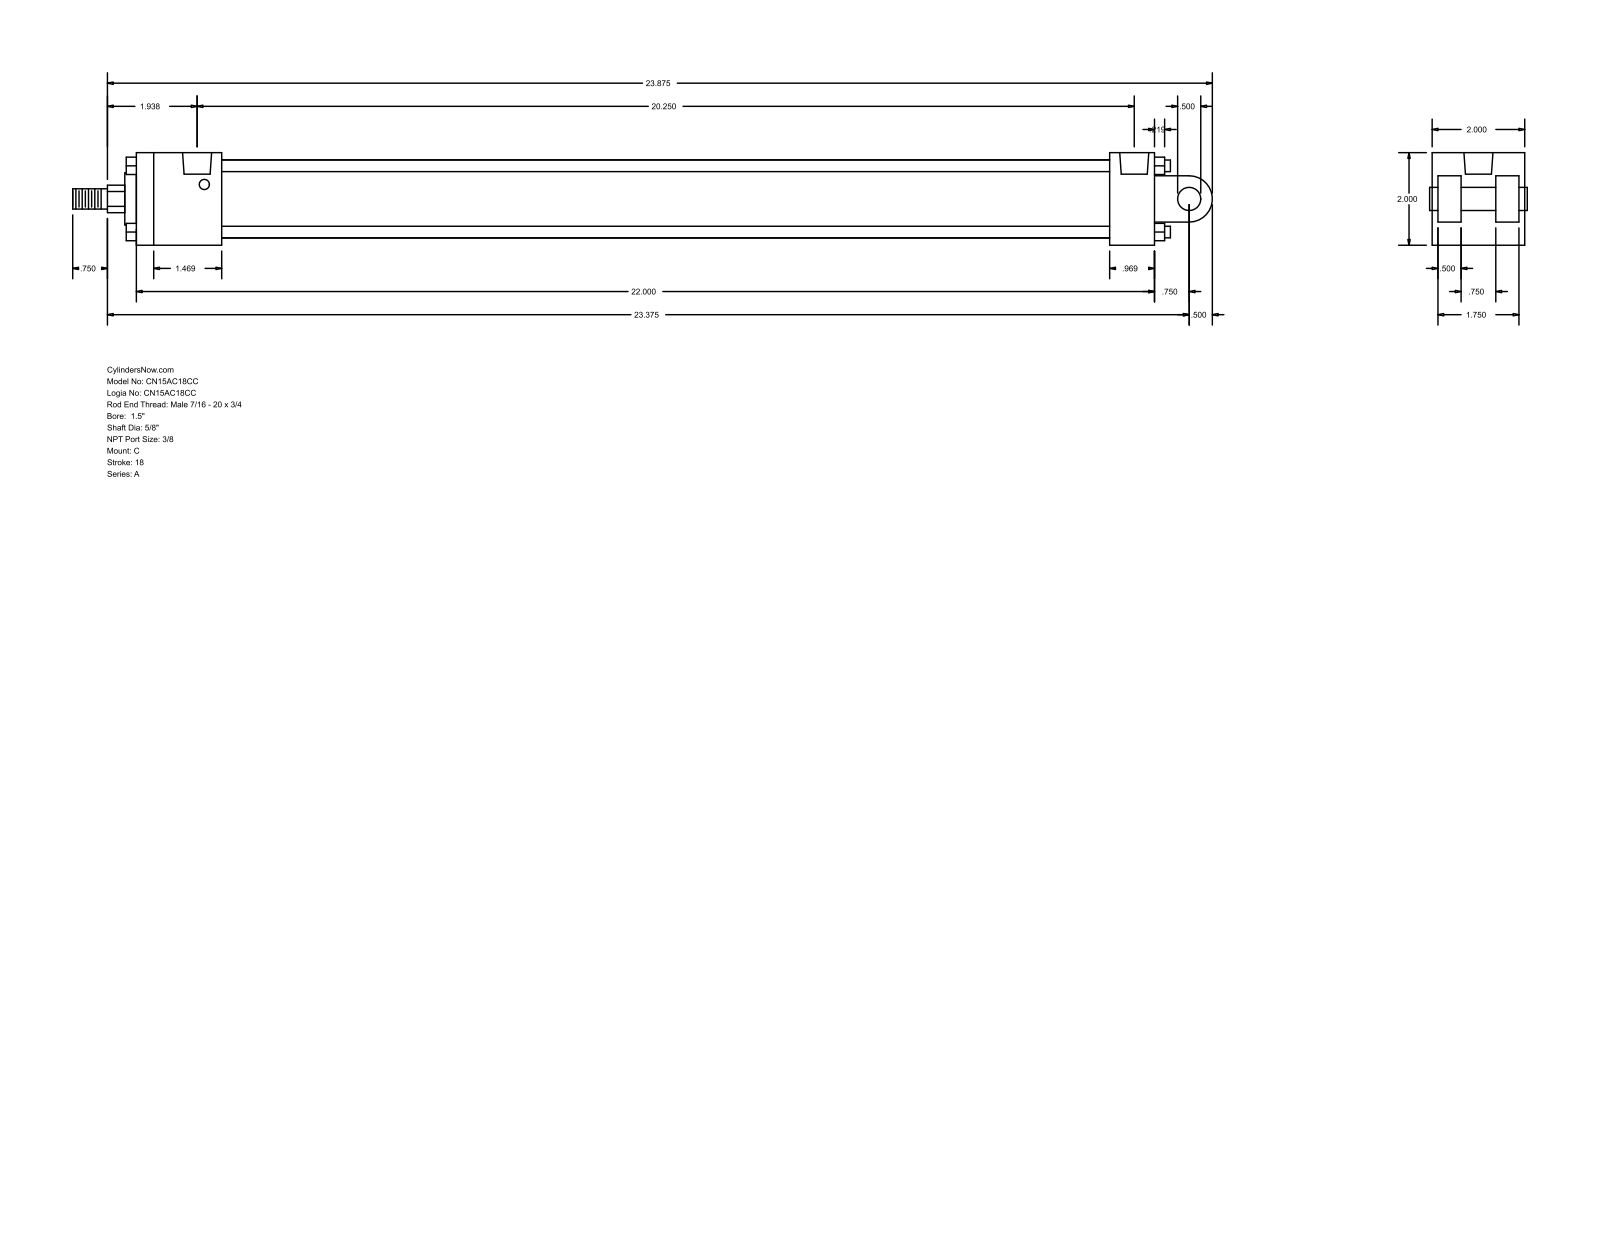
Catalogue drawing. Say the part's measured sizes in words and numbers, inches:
The part is named "A_C__0150_0.625". Its 3-D file was written by "GSSL Pune (CONFIG_CONTROL_DESIGN)". It is 0 solids with 135 faces: 102 planar, 33 cylindrical and 0 other. Overall it measures 24.625 by 2 by 2 inches. Round holes: 4 of diameter 0.219, 2 of diameter 0.627. Round bosses or shafts: 4 of diameter 0.25, 1 of diameter 1.69, 1 of diameter 1.125, 1 of diameter 0.625, 1 of diameter 0.5, 1 of diameter 0.437. Partial cylindrical surfaces (rounded edges, fillets, slot ends): 1 of radius 0.297, 1 of radius 0.5. The main face-to-face distances are 2, 0.5, 22, 1.375, 0.125, 1.875, 0.625, 1.25, 21.031, 0.969. The hole center spacings are 0.156, 19.937, 20.094, 20.25.
